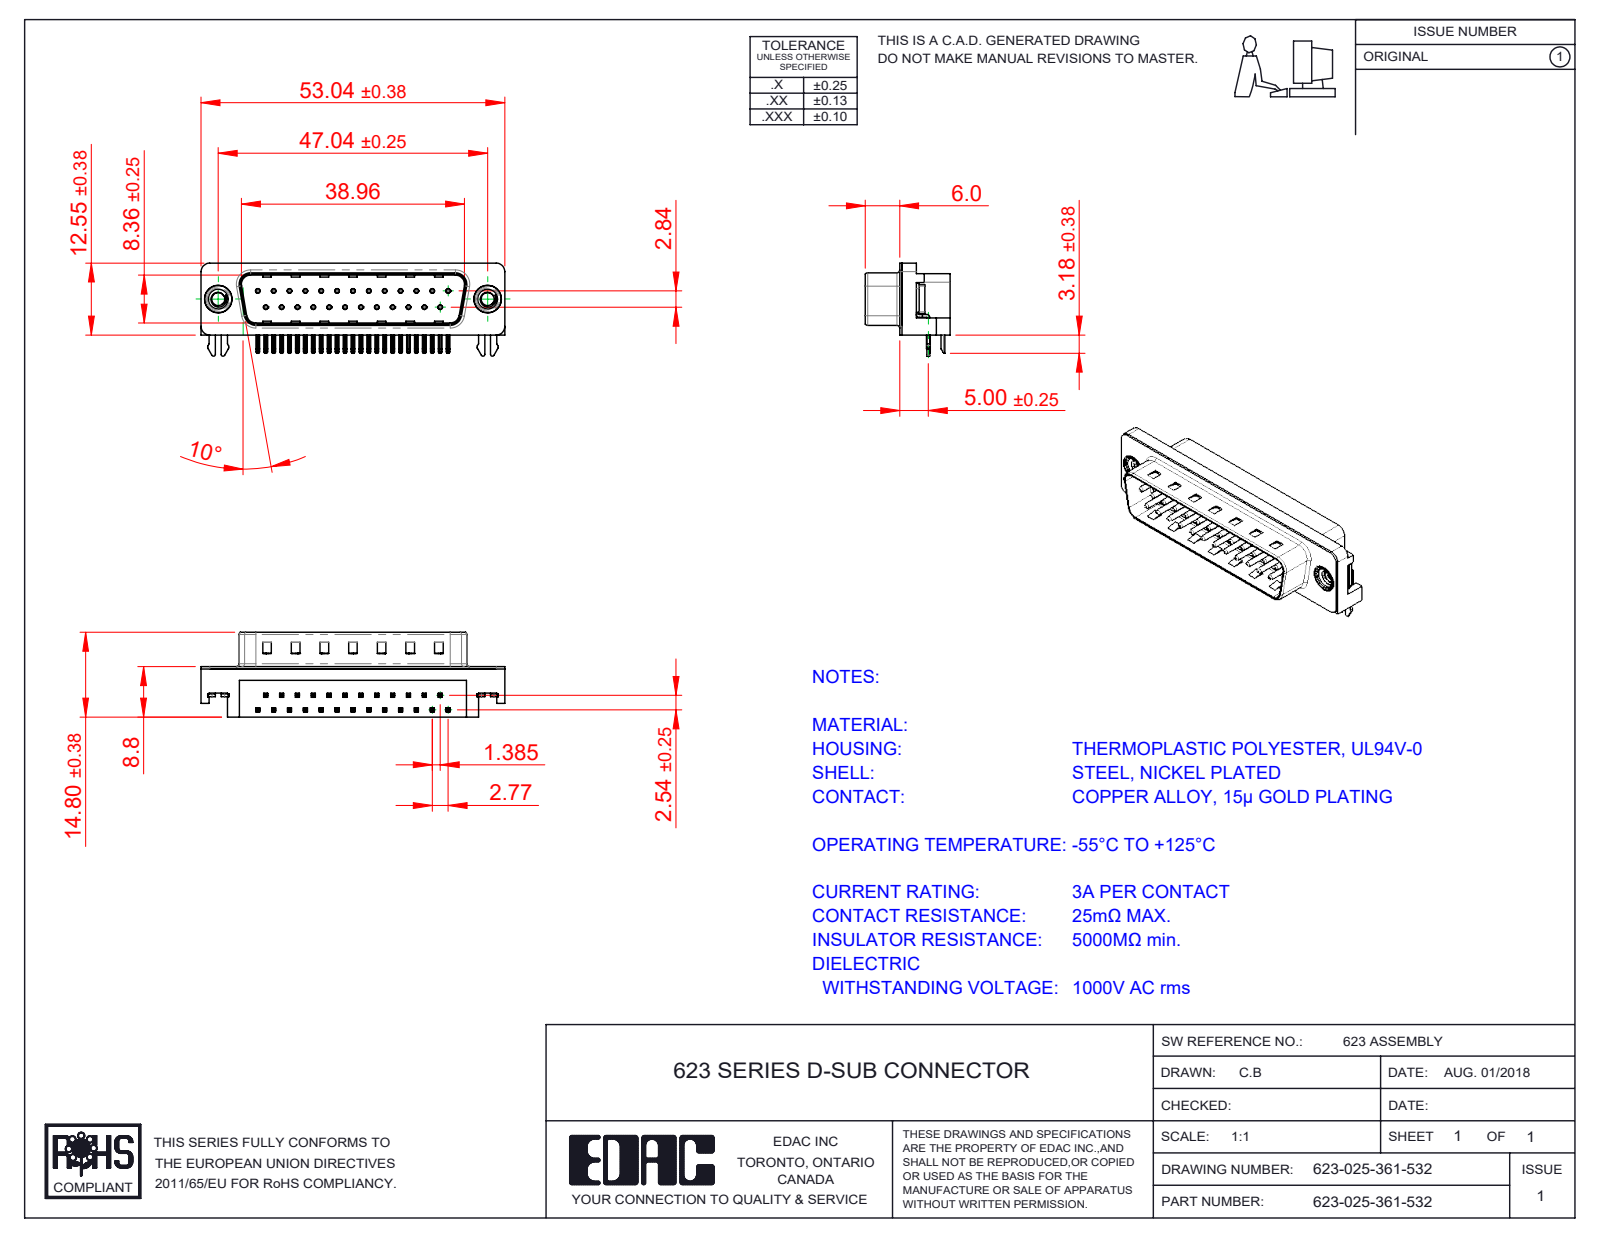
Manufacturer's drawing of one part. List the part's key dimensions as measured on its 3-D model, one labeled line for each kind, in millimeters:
Part name (STEP PRODUCT): 623 Contact Bottom; 623 Housing_25 Socket; 623 4-40 Threaded Rivet; 623 2 Prong Board Lock (+3 more)
STEP written by: SolidWorks 2016 (CONFIG_CONTROL_DESIGN)
Units: millimetres
Bodies: 31 solids, 2285 faces (1433 planar, 653 cylindrical, 199 other)
Overall size (bounding box): 53.04 × 16.25 × 14.8
Volume: 4 735 mm³ · Surface area: 6 779 mm²
Round holes (diameter × count): ⌀0.35 ×25, ⌀0.8 ×25, ⌀2.26 ×2, ⌀4 ×2, ⌀4.8 ×2, ⌀5 ×2
Round bosses / shafts (diameter × count): ⌀0.75 ×25, ⌀4.9 ×2, ⌀4.75 ×2, ⌀3.9 ×2
Partial cylindrical surfaces — rounded edges, fillets, slot ends (radius × count): R0.25 ×108, R0.12 ×50, R0.5 ×14, R1 ×8, R1.5 ×7, R0.32 ×4, R0.9 ×4, R1.6 ×4
Main face-to-face distances: 0.4, 8.4, 2.1, 1.7, 8.76, 10.46, 10.86, 10.35, 8.8, 5.9
Hole centre spacings: 3.16, 2.77, 11.08, 5.54, 8.31, 5.03, 13.85, 7.48
